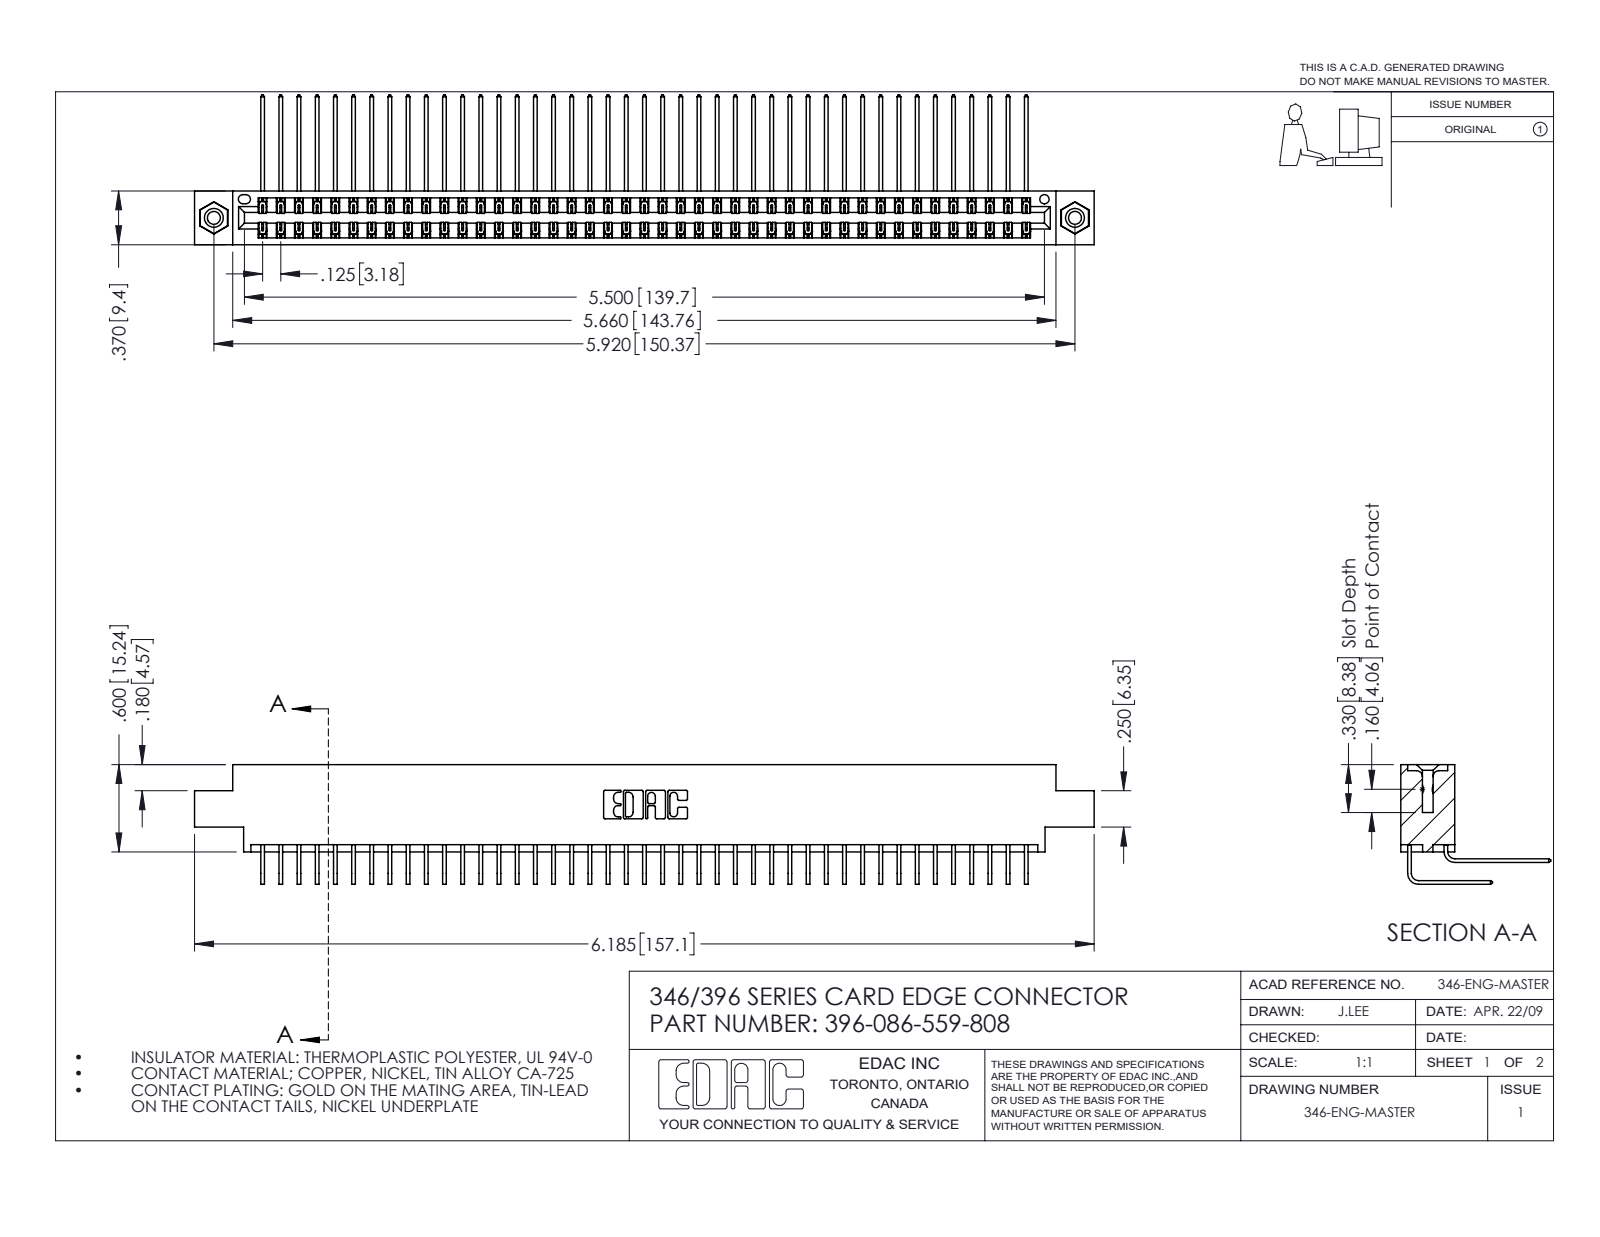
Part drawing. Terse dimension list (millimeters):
name: 345-250-001_345-250-003-102; 346 Part_0.170 Offset - 0.156 Dia-TI; 345-292-001_559 Tail - 2; 345-292-001_558 559 Tail - 1 (+1 more)
written by: SolidWorks 2016 (CONFIG_CONTROL_DESIGN)
unit: mm
bodies: 89 solids, 4830 faces (3294 planar, 1520 cylindrical, 16 other)
size: 157.1 × 26.2 × 20.9
volume: 15 700 mm³; area: 24 120 mm²
holes: 2× ⌀2.3, 2× ⌀3.2, 2× ⌀4, 1× ⌀1.6
bosses: 2× ⌀3.9
rounds: 129× R0.2, 22× R0.3, 6× R0.2, 6× R0.8, 3× R0.7, 2× R0.4, 2× R0.6, 2× R0.6
face distances: 1.2, 8.2, 0.6, 9.4, 6.4, 1.8, 7.6, 7, 5.6, 3.8
hole spacings: 6.2, 145.1, 150.4
